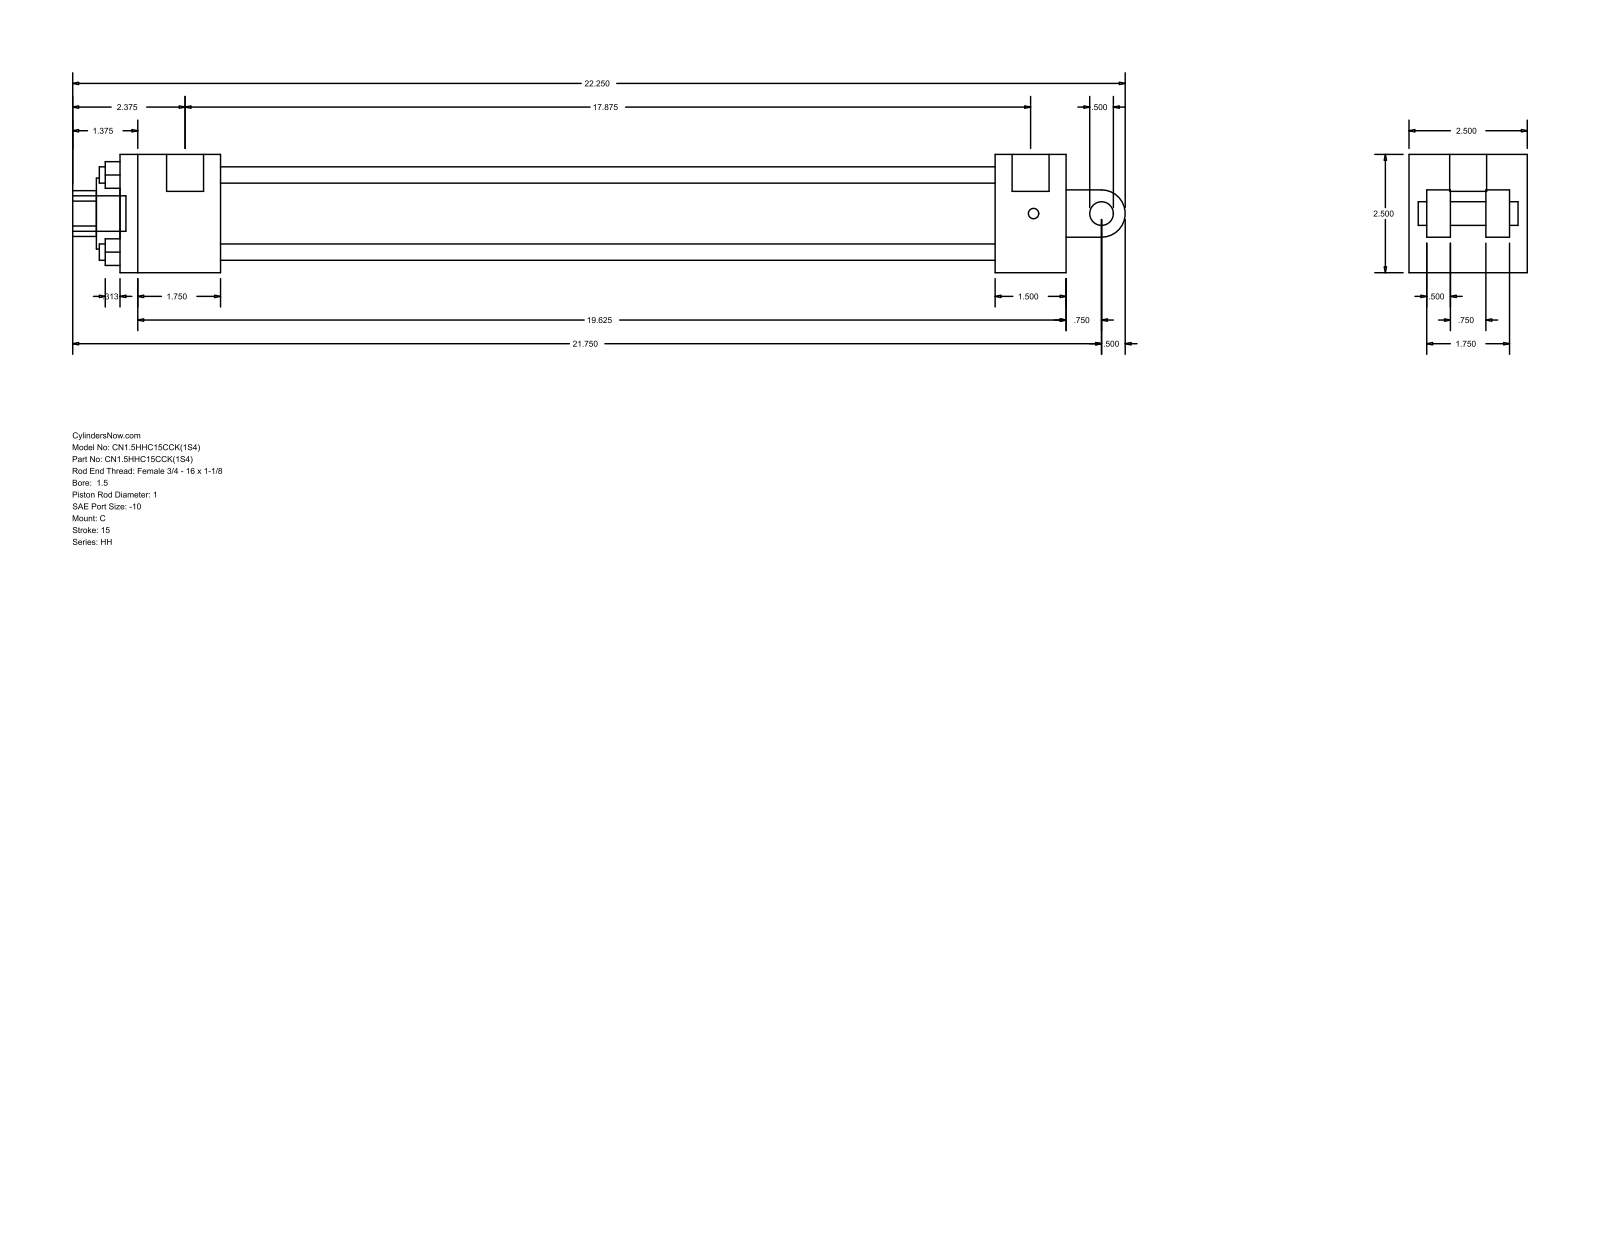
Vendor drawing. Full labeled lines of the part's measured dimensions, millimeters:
Part name (STEP PRODUCT): HH_C__0150_1
STEP written by: GSSL Pune (CONFIG_CONTROL_DESIGN)
Units: millimetres
Bodies: 0 solids, 99 faces (70 planar, 29 cylindrical, 0 other)
Overall size (bounding box): 565.15 × 63.5 × 63.5
Round holes (diameter × count): ⌀8.76 ×4, ⌀5.56 ×2, ⌀19.84 ×1, ⌀25.4 ×1, ⌀38.1 ×1, ⌀44.45 ×1
Round bosses / shafts (diameter × count): ⌀5.56 ×2, ⌀19.84 ×1, ⌀19.05 ×1, ⌀12.7 ×1
Partial cylindrical surfaces — rounded edges, fillets, slot ends (radius × count): R12.29 ×1, R12.7 ×1
Main face-to-face distances: 63.5, 53.98, 415.92, 454.02, 38.1, 469.9, 508, 12.7, 9.52, 22.22
Hole centre spacings: 29.27, 41.4, 58.55, 1.59
